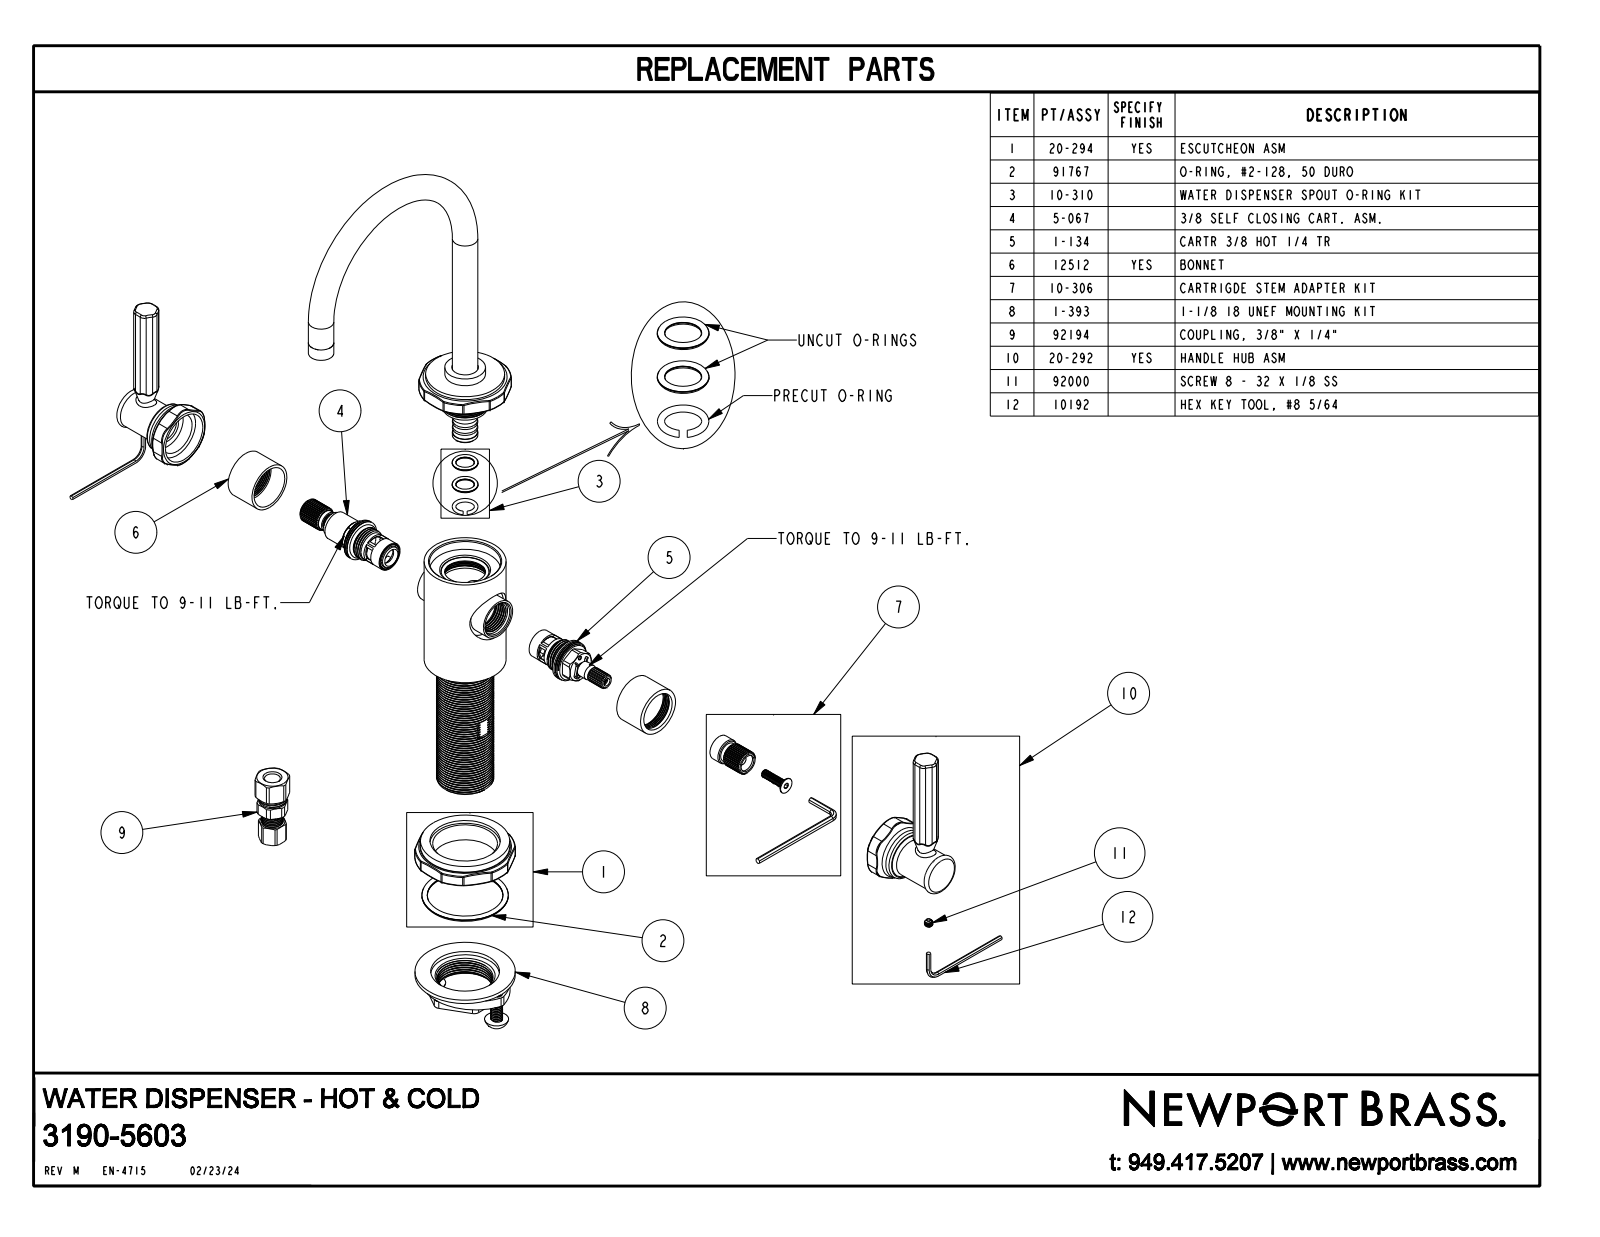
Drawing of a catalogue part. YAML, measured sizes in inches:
part_name: "3190-5603"
step_written_by: "CREO PARAMETRIC BY PTC INC, 2018400 (CONFIG_CONTROL_DESIGN)"
units: inches
bodies: {solids: 1, faces: 434, planar: 52, cylindrical: 84, other: 298}
overall_size: [9.275, 5.195, 5.125]
volume: 12.18
surface_area: 59.73
round_holes:
  - {diameter: 1, count: 1}
round_bosses_or_shafts:
  - {diameter: 0.5, count: 2}
  - {diameter: 1.75, count: 1}
  - {diameter: 1.61, count: 1}
  - {diameter: 1.55, count: 1}
  - {diameter: 0.97, count: 1}
  - {diameter: 0.8, count: 1}
  - {diameter: 0.76, count: 1}
partial_cylinders:
  - {radius: 0.08, count: 24}
  - {radius: 0.12, count: 12}
  - {radius: 0.31, count: 6}
  - {radius: 0.909, count: 1}
  - {radius: 0.988, count: 1}
face_to_face_distances: [3.145, 0.468, 3.676, 0.076, 1.814, 0.468, 3.208, 4.144, 5.125, 0.425]
